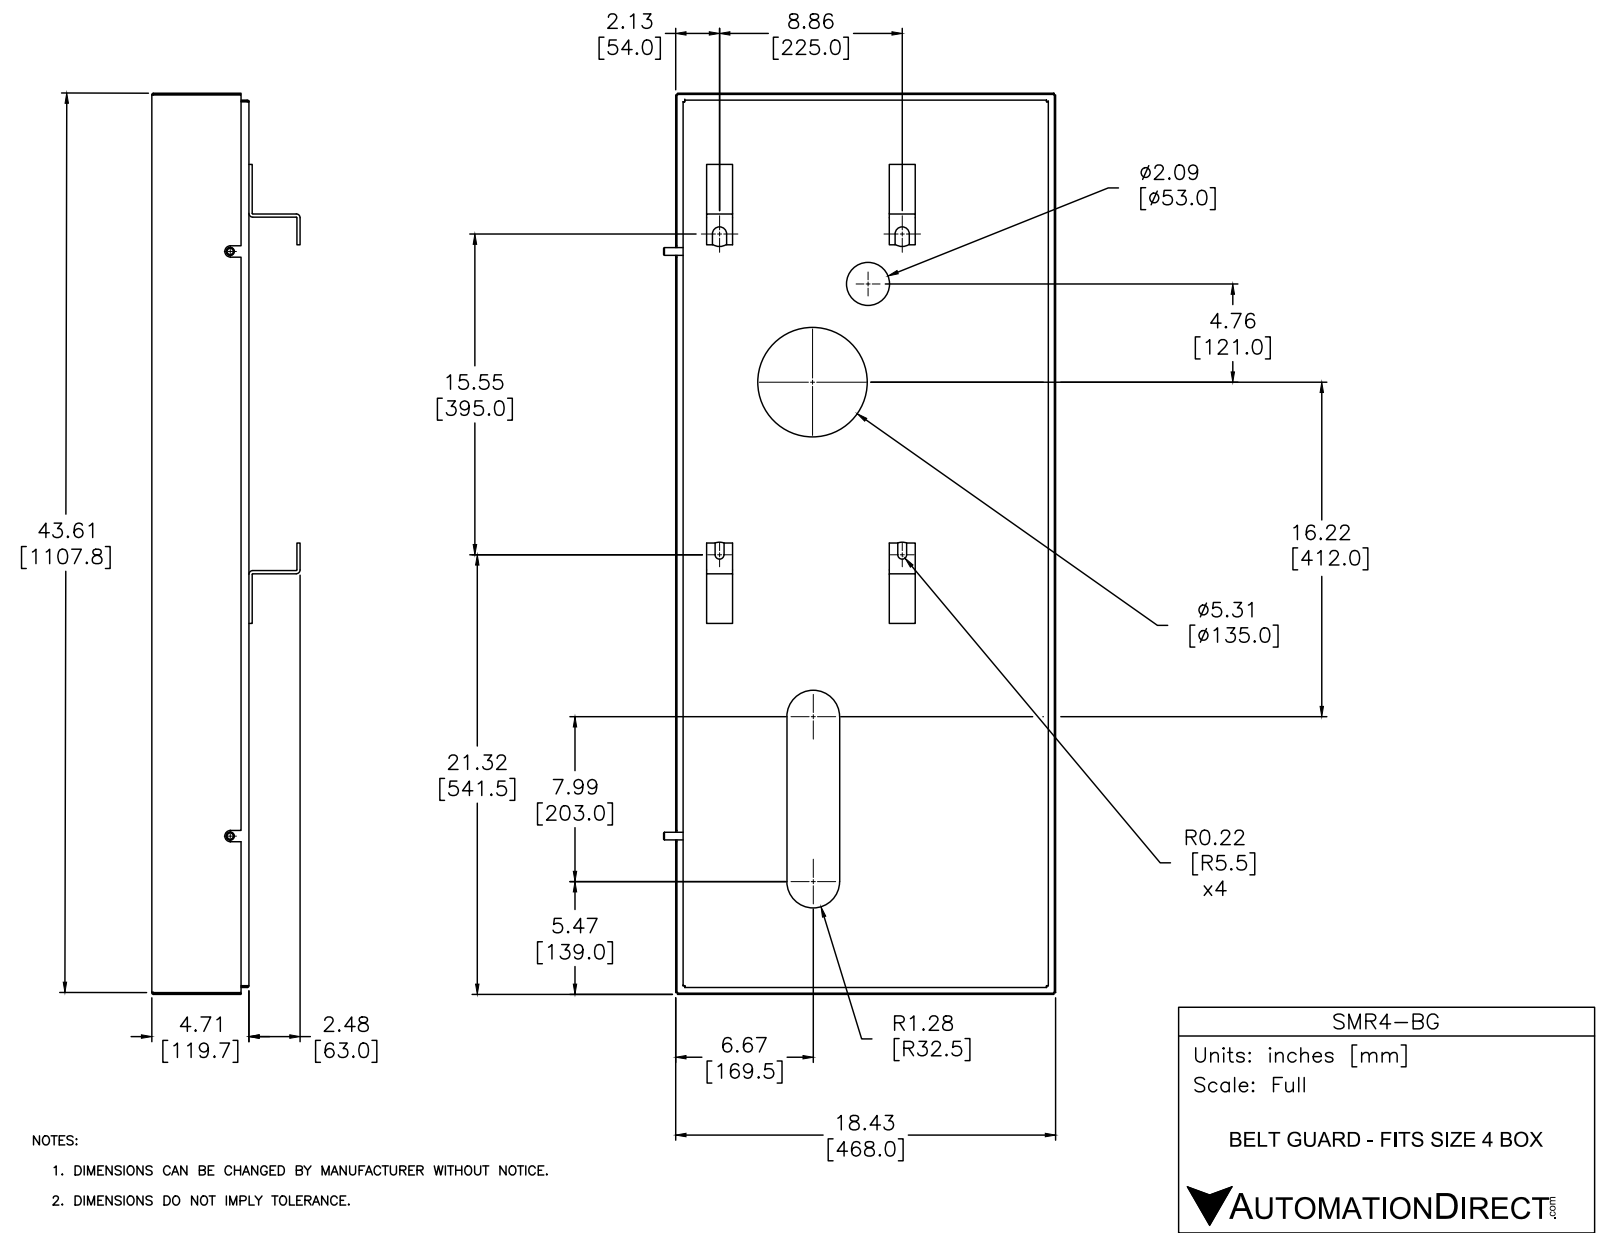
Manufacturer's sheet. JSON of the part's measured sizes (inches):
{"part_name": "SMR4-BG", "step_written_by": "SolidWorks 2016 (AUTOMOTIVE_DESIGN)", "units": "inches", "bodies": {"solids": 8, "faces": 202, "planar": 122, "cylindrical": 60, "other": 20}, "overall_size": [43.701, 19.012, 7.195], "volume_in3": 134.4, "surface_area_in2": 4478, "round_holes": [[1.22, 4], [0.394, 2], [2.087, 1], [5.315, 1]], "round_bosses_or_shafts": [[0.374, 2]], "partial_cylinders_radius": [[0.029, 12], [0.088, 8], [0.186, 4], [0.217, 2], [0.276, 2], [0.344, 2], [1.28, 2]], "face_to_face_distances": [0.059, 4.656, 4.715, 4.596, 18.366, 0.354, 18.012, 18.425, 18.307, 43.642], "hole_center_spacings": [8.858, 15.551, 17.897, 2.932, 5.474, 7.601, 8.4, 8.482]}
